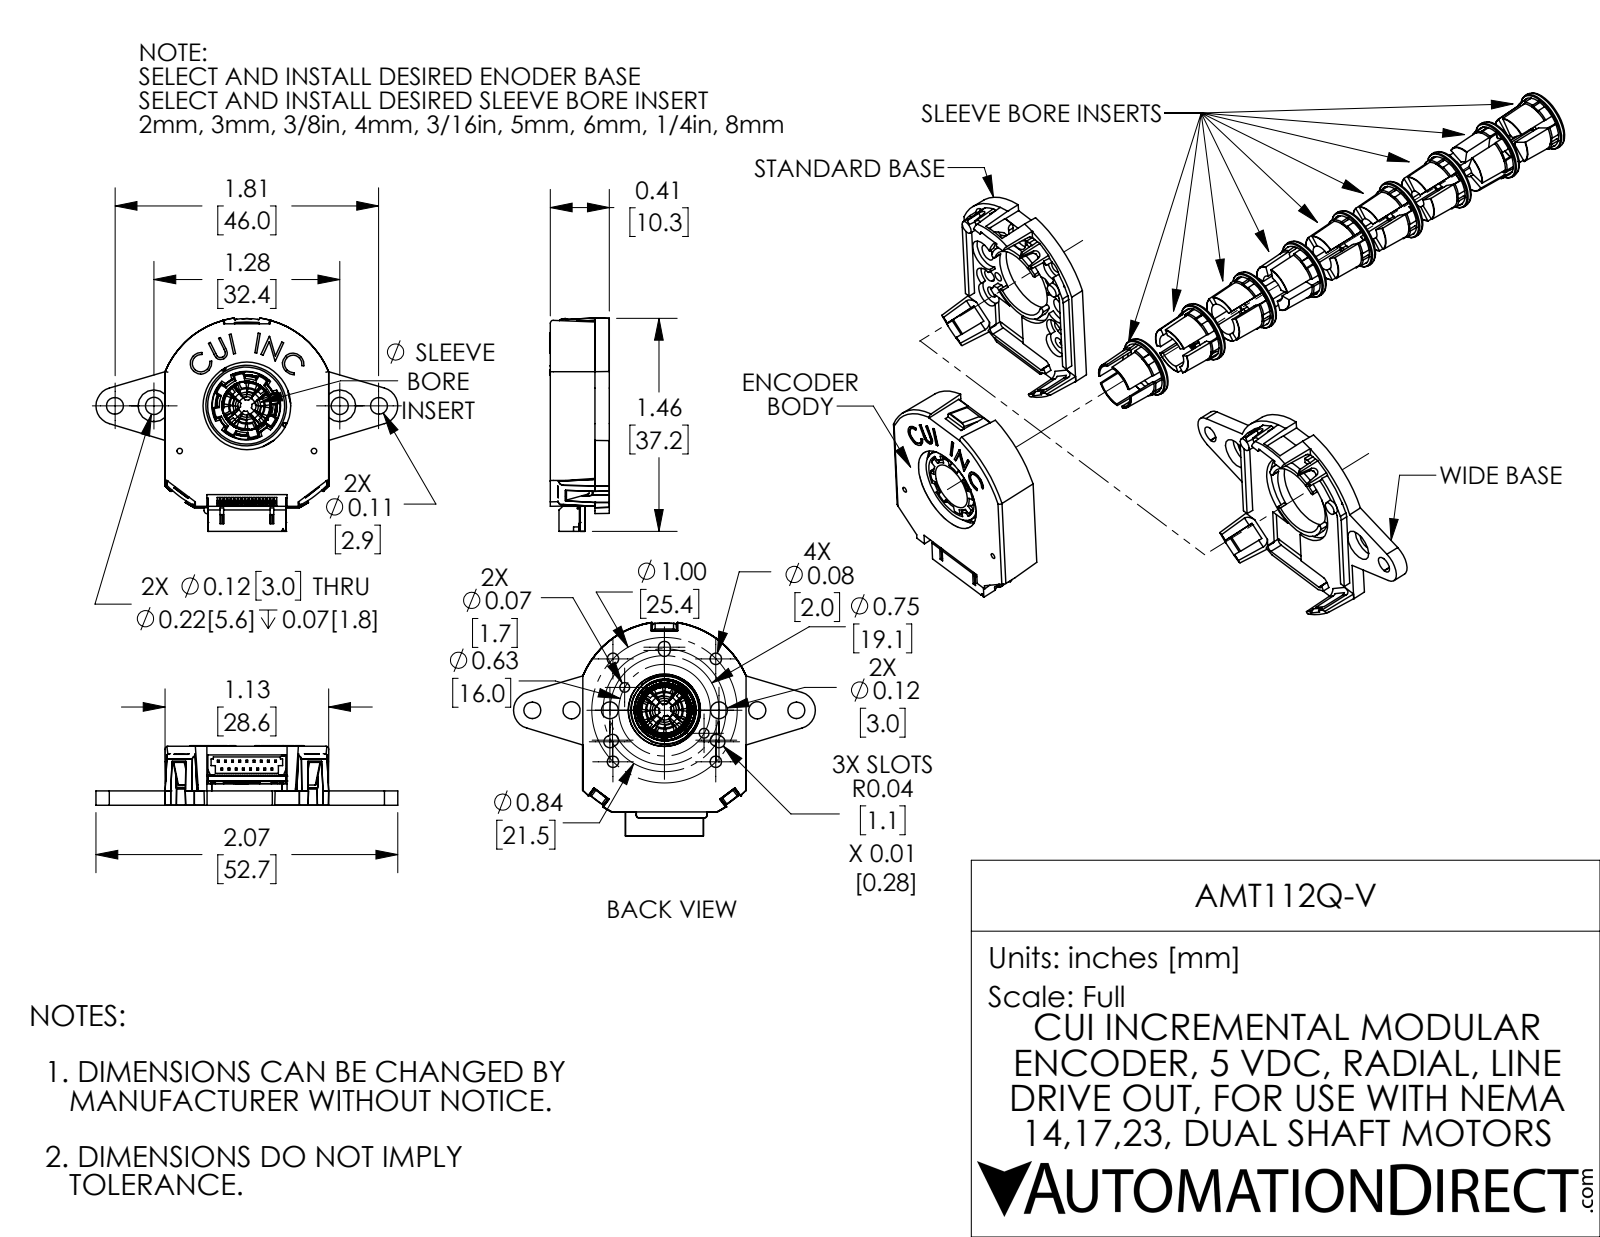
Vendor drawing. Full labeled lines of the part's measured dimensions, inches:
Part name (STEP PRODUCT): AMT112S-V r1c1 xt
STEP written by: SolidWorks 2017 (AUTOMOTIVE_DESIGN)
Units: inches
Bodies: 16 solids, 4253 faces (1956 planar, 1559 cylindrical, 738 other)
Overall size (bounding box): 5.467 × 4.573 × 1.467
Volume: 0.564 in³ · Surface area: 26.2 in²
Round holes (diameter × count): ⌀0.026 ×168, ⌀0.031 ×4, ⌀0.037 ×4, ⌀0.079 ×4, ⌀0.031 ×2, ⌀0.063 ×2, ⌀0.067 ×2, ⌀0.091 ×2, ⌀0.116 ×2, ⌀0.118 ×2, ⌀0.161 ×2, ⌀0.177 ×2
Round bosses / shafts (diameter × count): ⌀0.059 ×4, ⌀0.051 ×4, ⌀0.413 ×2, ⌀0.094 ×2, ⌀0.763 ×1, ⌀0.465 ×1, ⌀0.356 ×1
Partial cylindrical surfaces — rounded edges, fillets, slot ends (radius × count): R0.379 ×64, R0.039 ×30, R0.498 ×29, R0.079 ×11, R0.016 ×8, R0.02 ×6, R0.041 ×6, R0.012 ×4
Main face-to-face distances: 0.057, 0.033, 0.098, 1.547, 1.58, 1.604, 1.638, 0.156, 1.448, 1.482
Hole centre spacings: 0.354, 0.5, 0.707, 0.085, 0.403, 0.487, 0.625, 0.718
